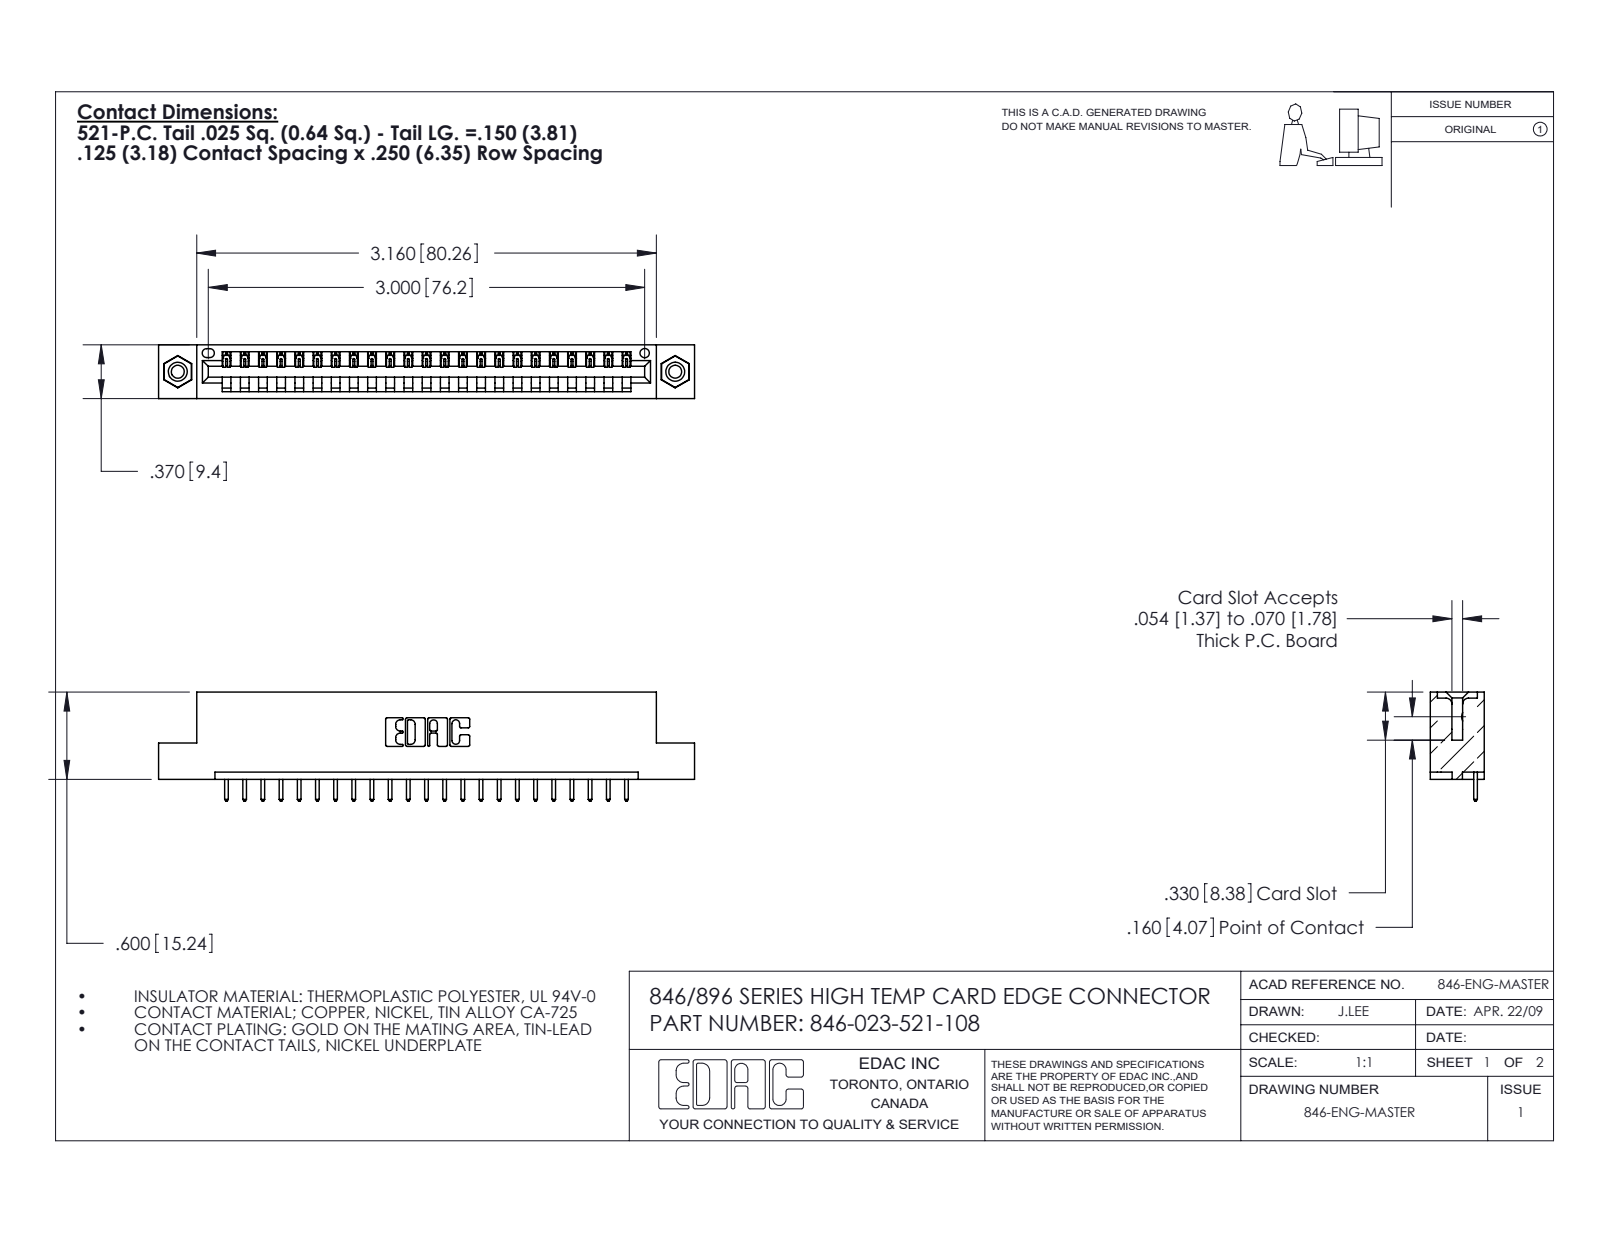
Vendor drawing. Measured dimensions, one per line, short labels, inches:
name: 346-023-521-108; 345-250-001_345-250-003-102; 346 Part_Flush Mounting Lugs - 0.156 Dia-TI; 345-292-001_345-293-121
written by: SolidWorks 2016 (CONFIG_CONTROL_DESIGN)
unit: in
bodies: 26 solids, 1516 faces (1028 planar, 472 cylindrical, 16 other)
size: 3.685 × 0.75 × 0.37
volume: 0.534 in³; area: 16.28 in²
holes: 2× ⌀0.089, 2× ⌀0.125, 2× ⌀0.156, 1× ⌀0.064
bosses: 2× ⌀0.155
rounds: 46× R0.006, 46× R0.01, 22× R0.01, 6× R0.007, 6× R0.031, 3× R0.026, 2× R0.031, 2× R0.04
face distances: 0.048, 0.322, 0.37, 0.25, 0.072, 0.298, 0.025, 0.148, 0.222, 0.1
hole spacings: 0.246, 3.212, 3.42
